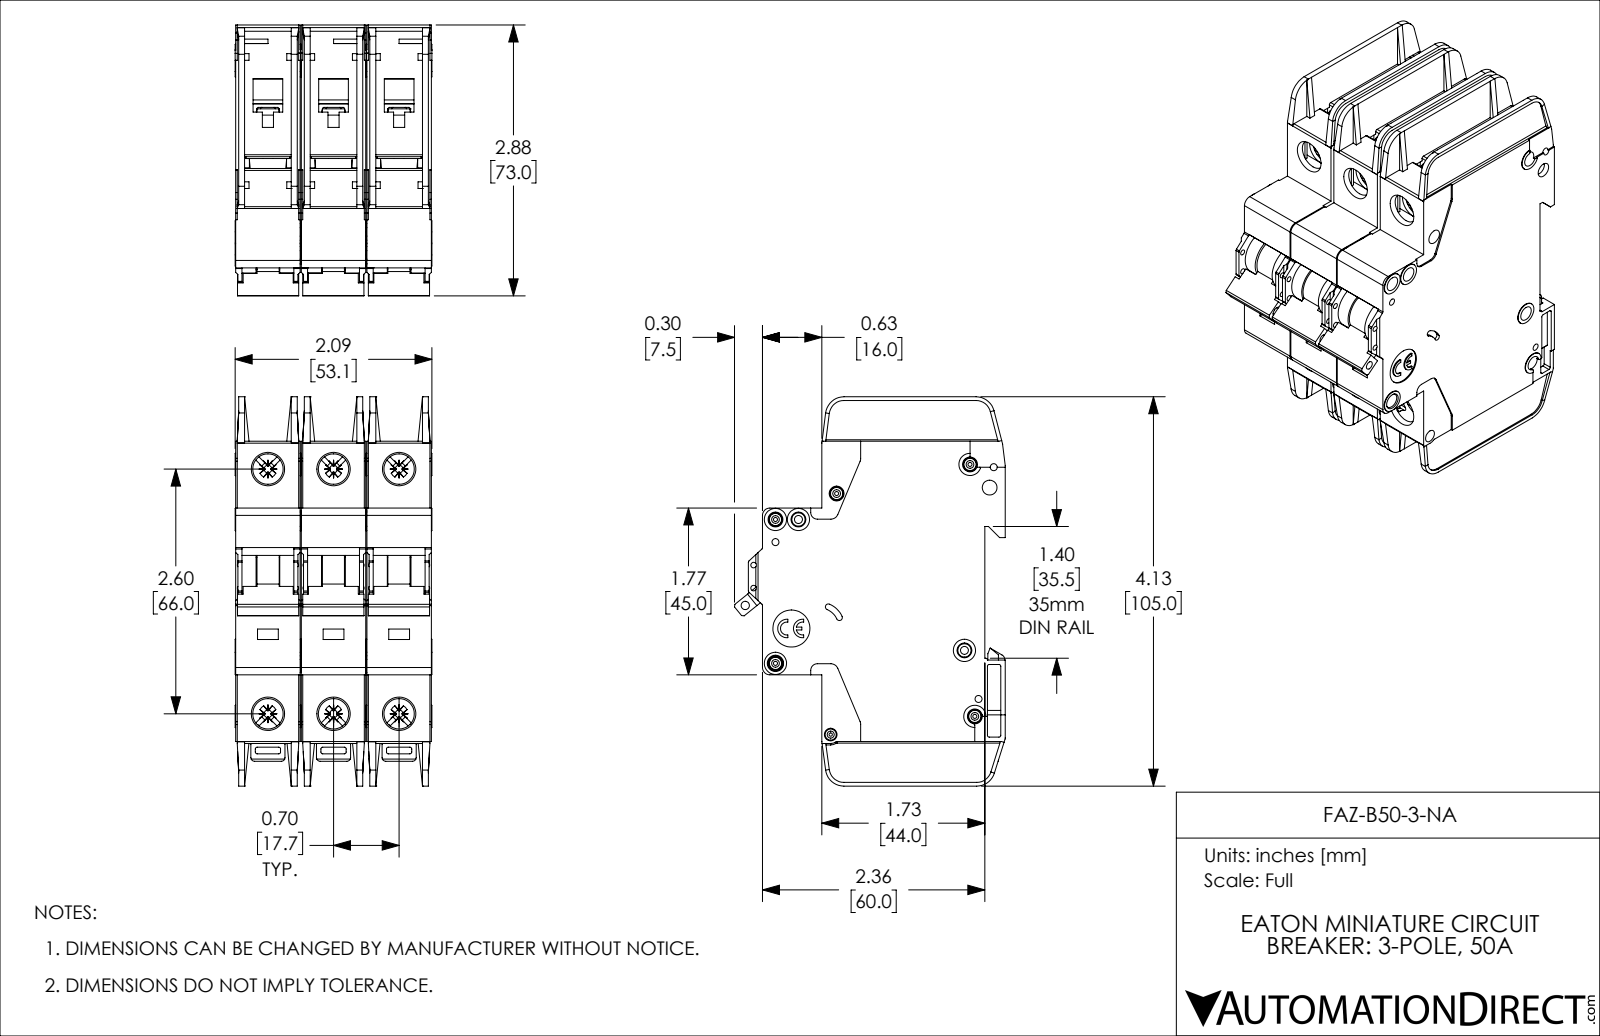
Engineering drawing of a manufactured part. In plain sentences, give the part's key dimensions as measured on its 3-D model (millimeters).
The part is named "FAZ-B50-3-NA". Its 3-D file was written by "SolidWorks 2019 (AUTOMOTIVE_DESIGN)". It is 3 solids with 3381 faces: 2013 planar, 1071 cylindrical and 297 other. Overall it measures 105 by 73.1 by 53.1 millimeters. Its volume is 230 200 cubic millimeters and its surface area 79 350 square millimeters. Round holes: 8 of diameter 4, 6 of diameter 8.2, 5 of diameter 1.1, 4 of diameter 1.9, 2 of diameter 1.5, 2 of diameter 2.2, 1 of diameter 0.9, 1 of diameter 2.3, 1 of diameter 2.5, 1 of diameter 3.4, 1 of diameter 10. Round bosses or shafts: 5 of diameter 3.3, 4 of diameter 6, 4 of diameter 3, 3 of diameter 2.5. Partial cylindrical surfaces (rounded edges, fillets, slot ends): 72 of radius 0.5, 30 of radius 0.4, 18 of radius 1, 12 of radius 1.1, 12 of radius 2, 6 of radius 0.2, 6 of radius 0.3, 6 of radius 0.7. The main face-to-face distances are 17.7, 1.2, 35.4, 17.4, 15, 35.1, 18.9, 16.5, 2.7, 2.4. The hole center spacings are 17.7, 68.3, 66, 6.2, 13.6, 22.1, 35.4, 74.9.
